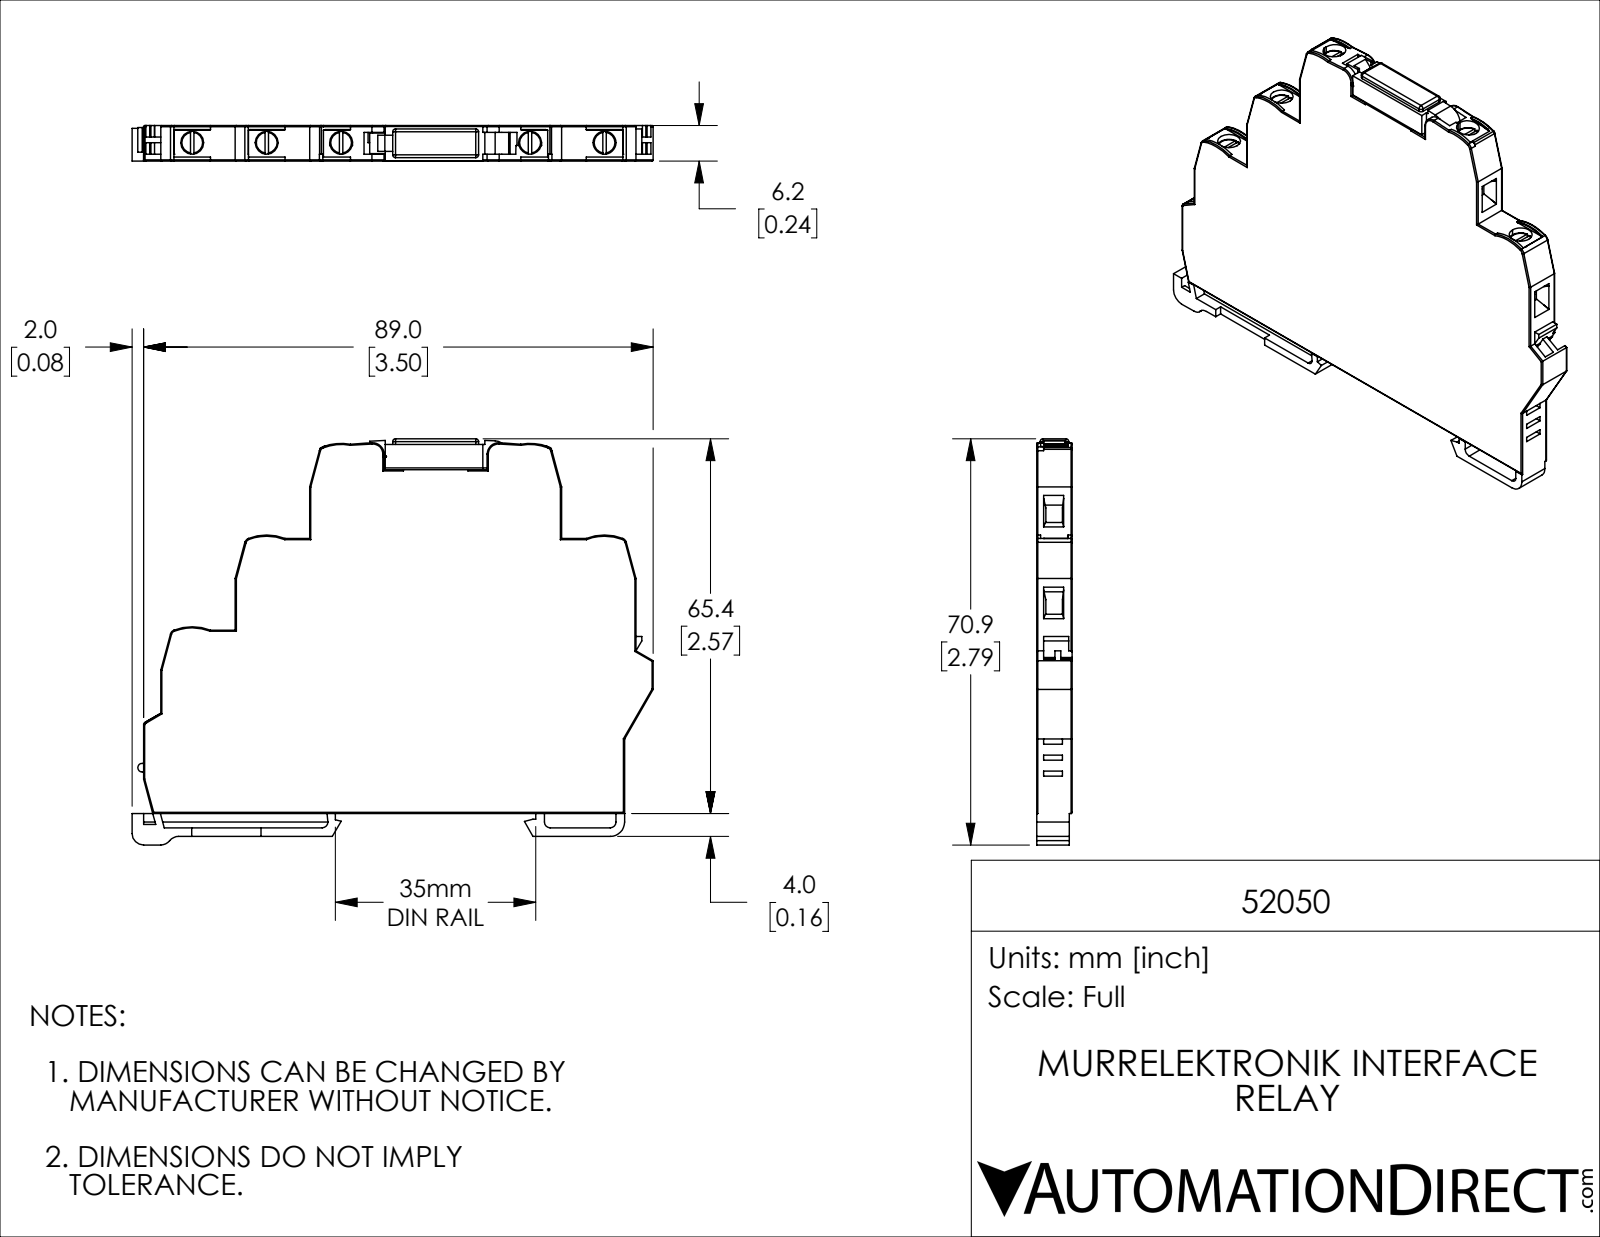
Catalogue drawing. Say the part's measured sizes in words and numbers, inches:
The part is named "52050". Its 3-D file was written by "SolidWorks 2019 (CONFIG_CONTROL_DESIGN)". It is 2 solids with 566 faces: 351 planar, 147 cylindrical and 68 other. Overall it measures 3.583 by 2.791 by 0.244 inches. Its volume is 1.706 cubic inches and its surface area 20.13 square inches. Round holes: 5 of diameter 0.157, 1 of diameter 0.075. Round bosses or shafts: 1 of diameter 0.079. Partial cylindrical surfaces (rounded edges, fillets, slot ends): 56 of radius 0.008, 11 of radius 0.02, 8 of radius 0.039, 6 of radius 0.079, 5 of radius 0.03, 5 of radius 0.346, 4 of radius 0.005, 3 of radius 0.016. The main face-to-face distances are 0.244, 0.059, 0.197, 0.098, 0.157, 0.118, 0.047, 0.02, 0.039, 2.362. The hole center spacings are 0.512, 1.811, 2.323, 1.024, 1.299, 2.835.
